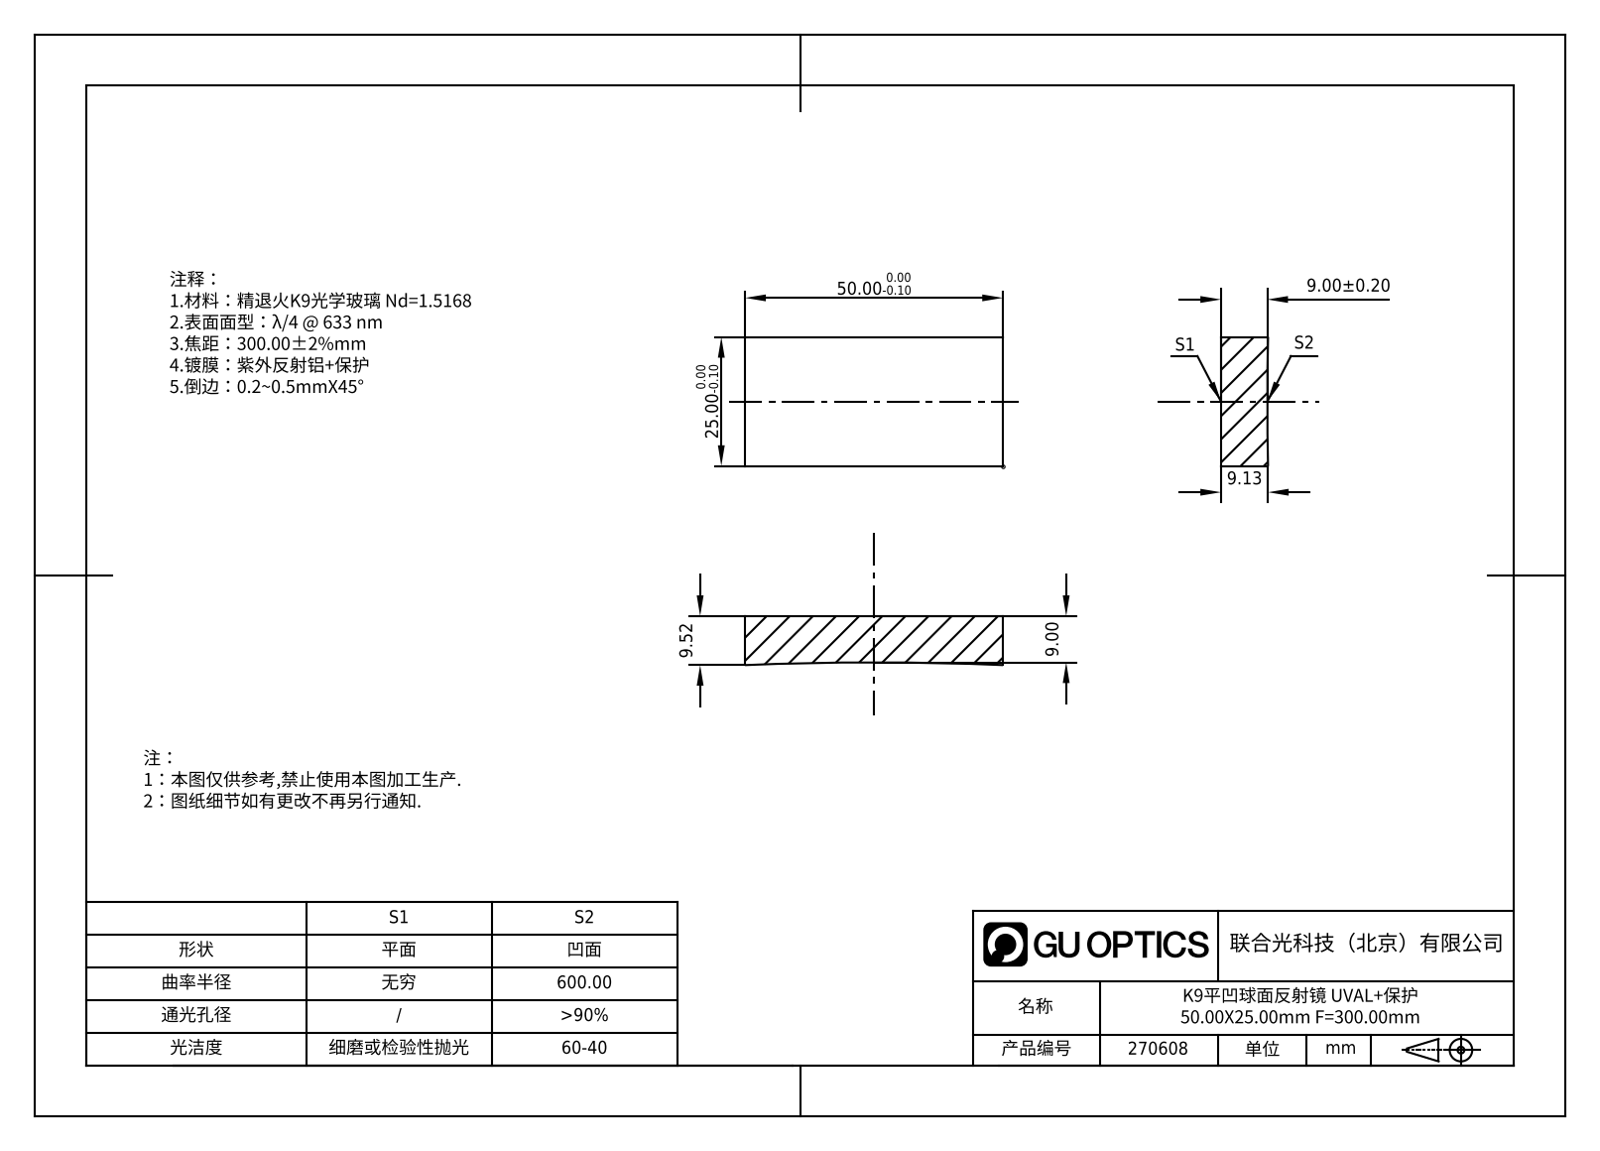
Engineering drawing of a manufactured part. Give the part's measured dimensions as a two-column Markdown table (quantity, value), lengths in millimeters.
| quantity | value |
| --- | --- |
| part name | GM13-50x25-300 |
| STEP written by | SolidWorks 2022 (AUTOMOTIVE_DESIGN) |
| units | millimeters |
| bodies | 1 solid, 7 faces (5 planar, 0 cylindrical, 2 other) |
| overall size | 50 × 25 × 9.65 |
| volume | 11 521 mm³ |
| surface area | 3 909 mm² |
| main face-to-face distances | 25, 50 |
